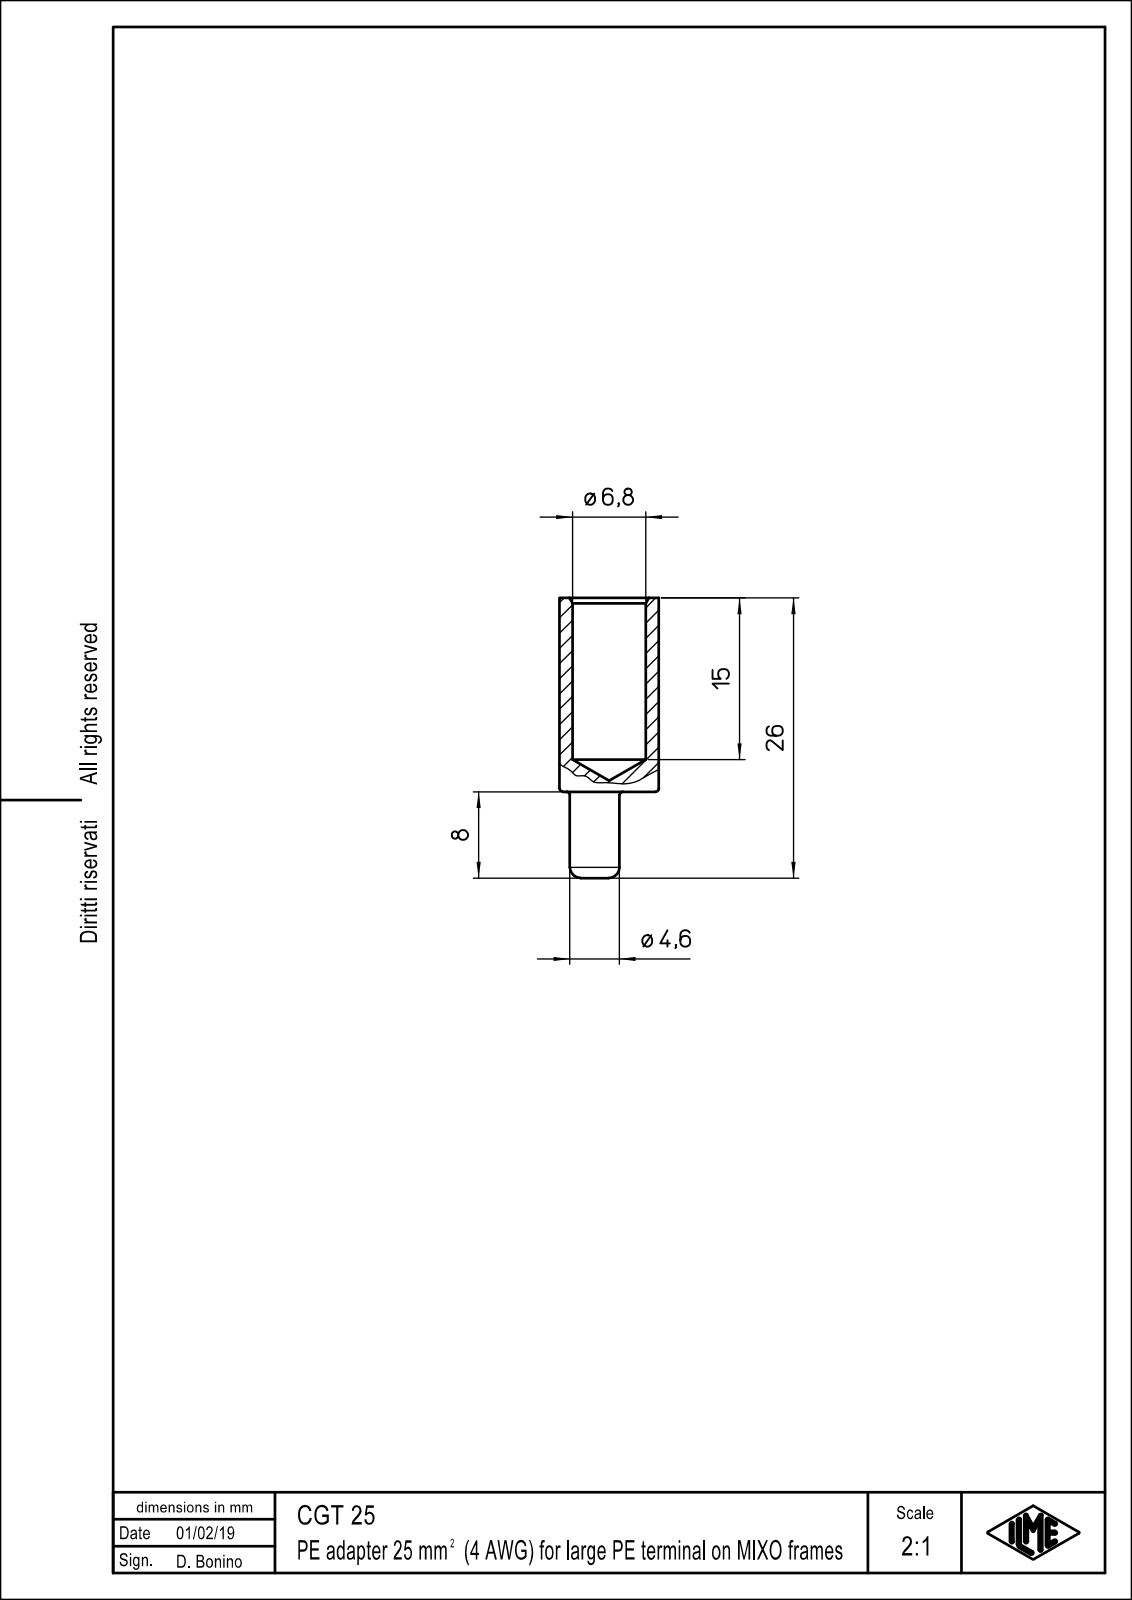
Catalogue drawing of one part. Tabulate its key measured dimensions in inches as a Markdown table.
| quantity | value |
| --- | --- |
| part name | CGT_25 |
| STEP written by | PTC Creo Elements/Direct Modeling 19.0B 21-Mar-2015 (C) Parametric Technology GmbH (AUTOMOTIVE_DESIGN) |
| units | inches |
| bodies | 1 solid, 19 faces (3 planar, 6 cylindrical, 10 other) |
| overall size | 1.024 × 0.362 × 0.362 |
| volume | 0.046 in³ |
| surface area | 1.671 in² |
| round holes (diameter × count) | 0.268 × 1 |
| round bosses / shafts (diameter × count) | 0.362 × 1, 0.181 × 1 |
| main face-to-face distances | 0.709, 1.024, 0.315 |
